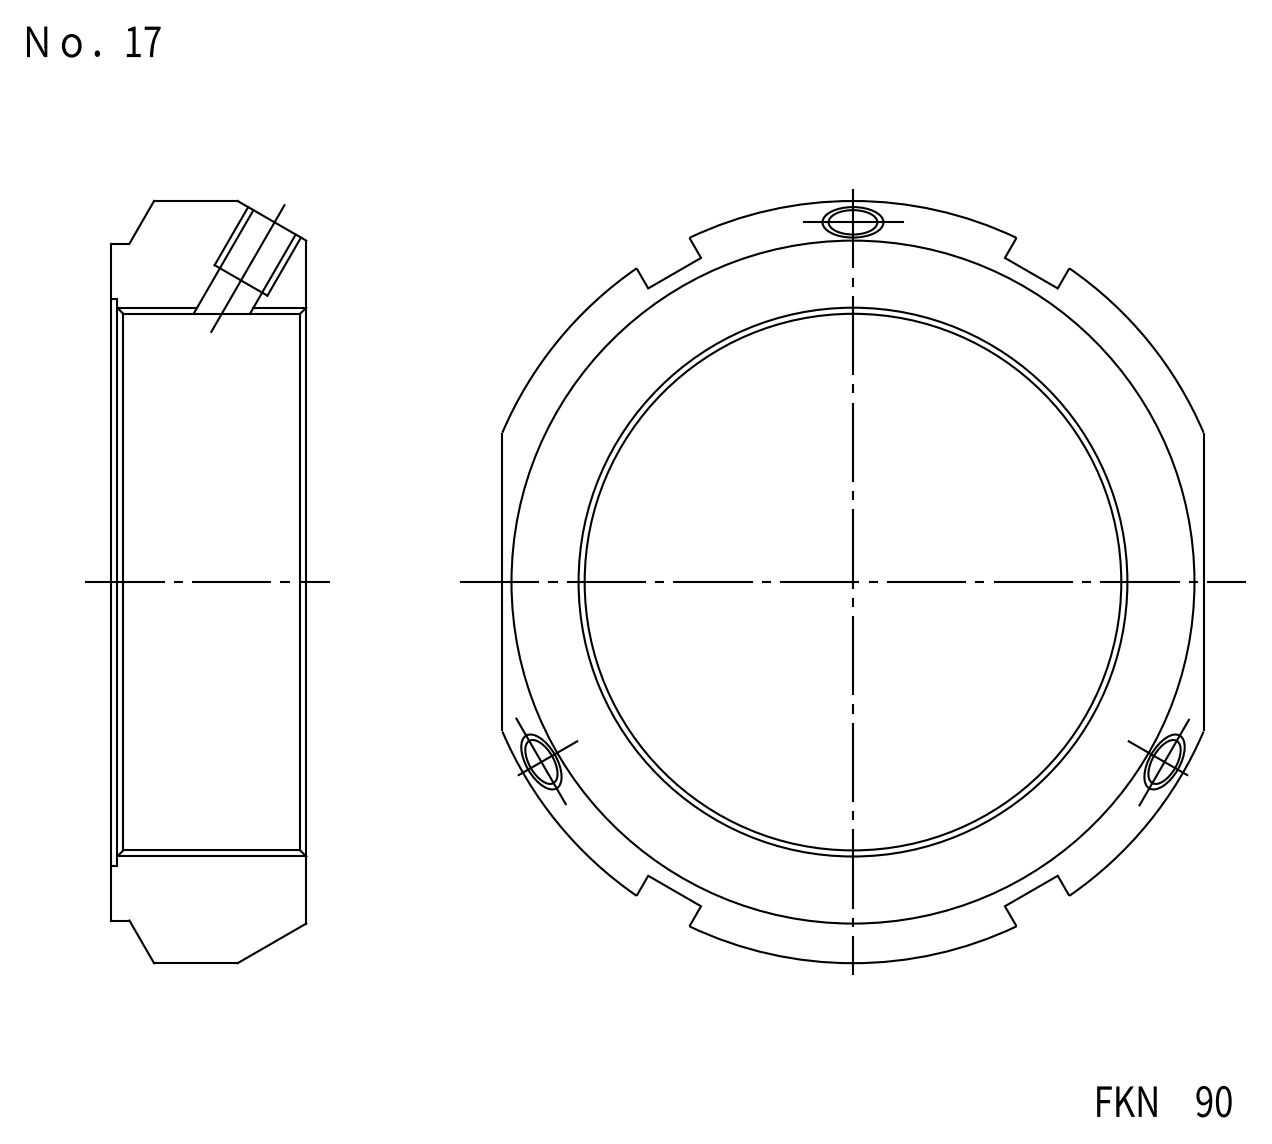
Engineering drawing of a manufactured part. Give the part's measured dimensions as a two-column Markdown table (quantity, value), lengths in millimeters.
| quantity | value |
| --- | --- |
| part name | FKD FKN90 |
| STEP written by | Autodesk Inventor LT (CONFIG_CONTROL_DESIGN) |
| units | millimeters |
| bodies | 1 solid, 37 faces (20 planar, 15 cylindrical, 2 other) |
| overall size | 125 × 115 × 32 |
| volume | 149 879 mm³ |
| surface area | 31 150 mm² |
| round holes (diameter × count) | 8.38 × 3, 10.2 × 3, 90 × 1, 93 × 1 |
| round bosses / shafts (diameter × count) | 111 × 1 |
| partial cylindrical surfaces (radius × count) | 62.5 × 1 |
| main face-to-face distances | 32, 115, 117, 1.5, 30.5, 10 |
